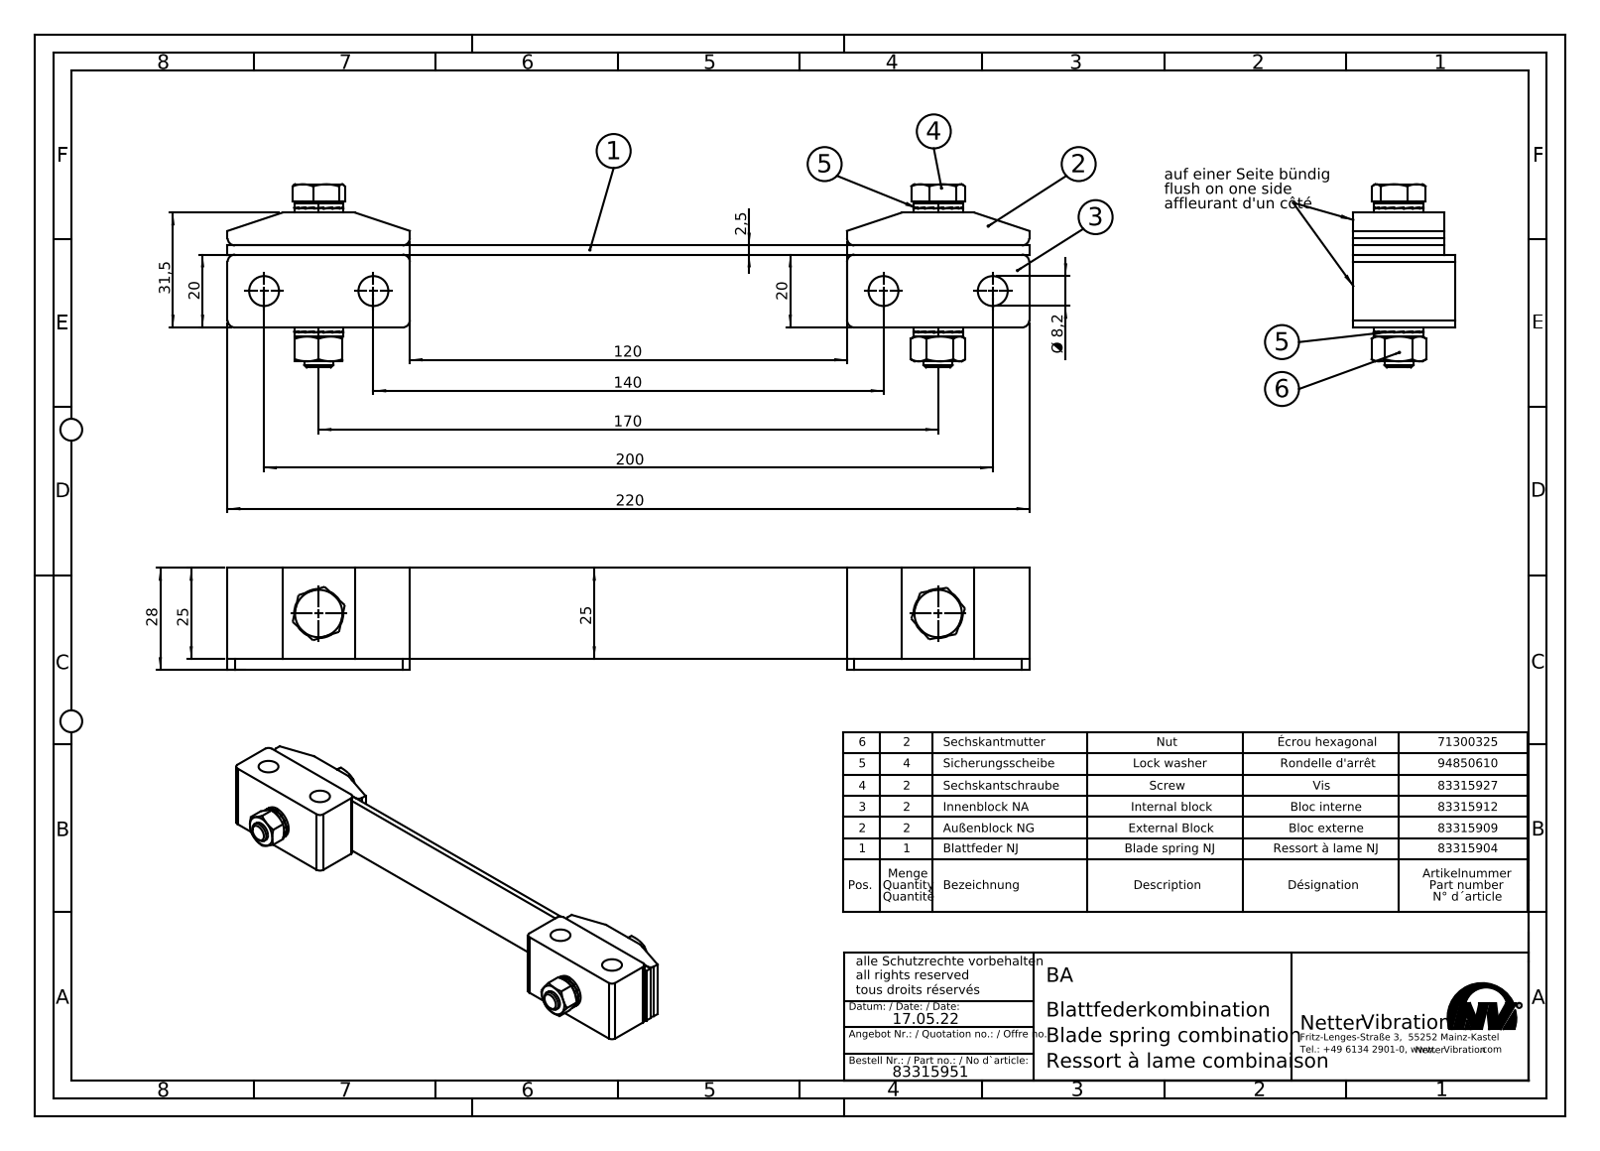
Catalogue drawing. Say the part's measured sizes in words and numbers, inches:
The part is named "Blattfederkombination BA # 83315951". Its 3-D file was written by "SolidWorks 2015 (AUTOMOTIVE_DESIGN)". It is 13 solids with 660 faces: 536 planar, 72 cylindrical and 52 other. Overall it measures 8.661 by 1.98 by 1.102 inches. Its volume is 5.334 cubic inches and its surface area 62.59 square inches. Round holes: 6 of diameter 0.323, 2 of diameter 0.268, 2 of diameter 0.315, 2 of diameter 0.335, 2 of diameter 0.343. Round bosses or shafts: 2 of diameter 0.531, 2 of diameter 0.512. Partial cylindrical surfaces (rounded edges, fillets, slot ends): 8 of radius 0.079, 4 of radius 0.02. The main face-to-face distances are 0.098, 0.886, 0.787, 1.102, 0.984, 0.453, 0.118, 1.24, 0.354, 6.693. The hole center spacings are 6.693, 1.181, 5.512, 7.874.
